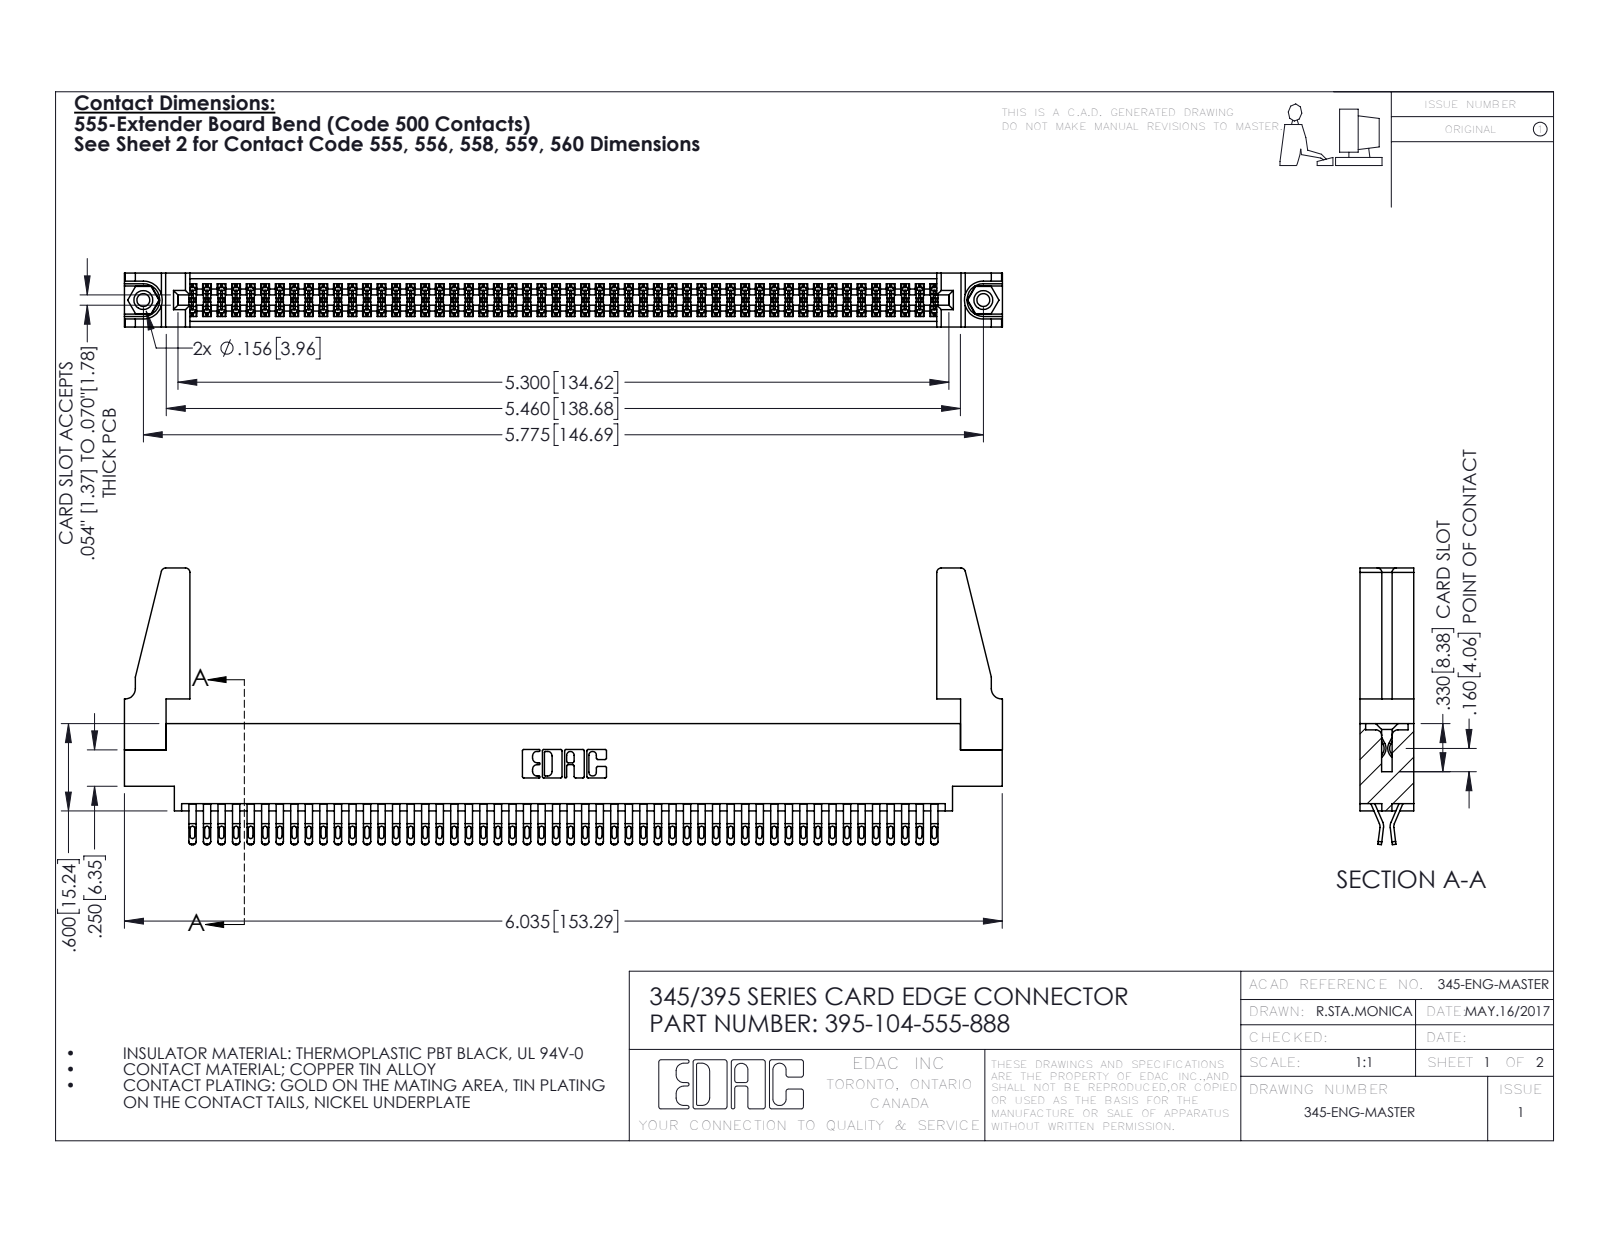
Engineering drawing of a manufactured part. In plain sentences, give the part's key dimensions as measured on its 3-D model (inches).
The part is named "345 Part_0.170 Offset - 0.156 Dia-TH; 345-220-078_345-220-088; 395-104-555-888; 345-250-001_345-250-001-102 (+1 more)". Its 3-D file was written by "SolidWorks 2016 (CONFIG_CONTROL_DESIGN)". It is 109 solids with 6078 faces: 3380 planar, 2682 cylindrical and 16 other. Overall it measures 6.036 by 1.902 by 0.37 inches. Its volume is 1.124 cubic inches and its surface area 41.75 square inches. Round holes: 2 of diameter 0.089, 2 of diameter 0.125, 2 of diameter 0.156, 1 of diameter 0.064. Round bosses or shafts: 2 of diameter 0.155. Partial cylindrical surfaces (rounded edges, fillets, slot ends): 260 of radius 0.016, 208 of radius 0.02, 156 of radius 0.006, 22 of radius 0.01, 8 of radius 0.03, 6 of radius 0.007, 6 of radius 0.031, 3 of radius 0.026. The main face-to-face distances are 0.072, 0.298, 0.37, 0.025, 0.098, 0.272, 0.2, 0.225, 0.175, 0.149. The hole center spacings are 0.27, 5.539, 5.775.
